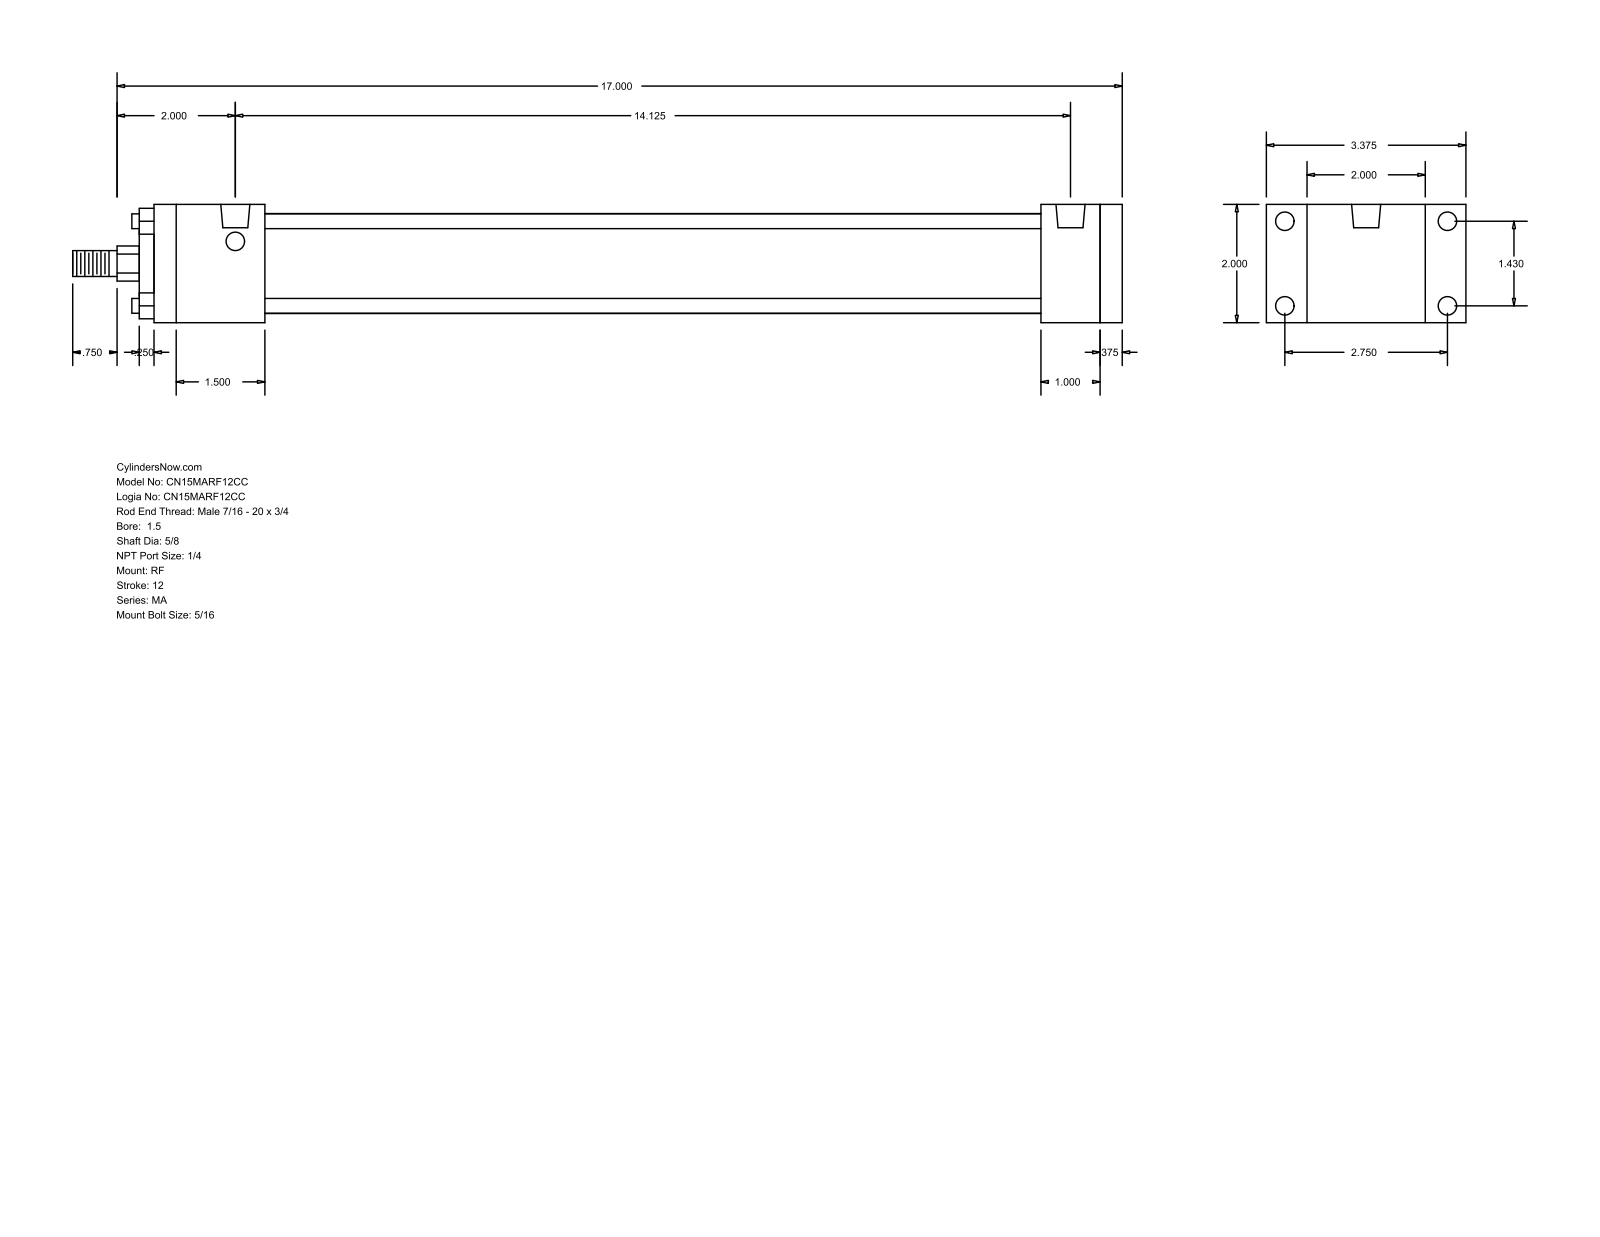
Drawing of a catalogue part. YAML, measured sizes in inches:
part_name: "MA_RF__0150_0.625"
step_written_by: "GSSL Pune (CONFIG_CONTROL_DESIGN)"
units: inches
bodies: {solids: 0, faces: 92, planar: 64, cylindrical: 28, other: 0}
overall_size: [17.75, 3.375, 2]
round_holes:
  - {diameter: 0.313, count: 8}
  - {diameter: 0.492, count: 2}
round_bosses_or_shafts:
  - {diameter: 0.25, count: 4}
  - {diameter: 1.69, count: 1}
  - {diameter: 1.125, count: 1}
  - {diameter: 0.625, count: 1}
  - {diameter: 0.437, count: 1}
partial_cylinders:
  - {radius: 0.297, count: 1}
face_to_face_distances: [2, 0.375, 16.375, 16, 15, 1, 1.375, 1.875, 13.125, 14.125]
hole_center_spacings: [1.43, 2.75, 3.099, 14.125]
